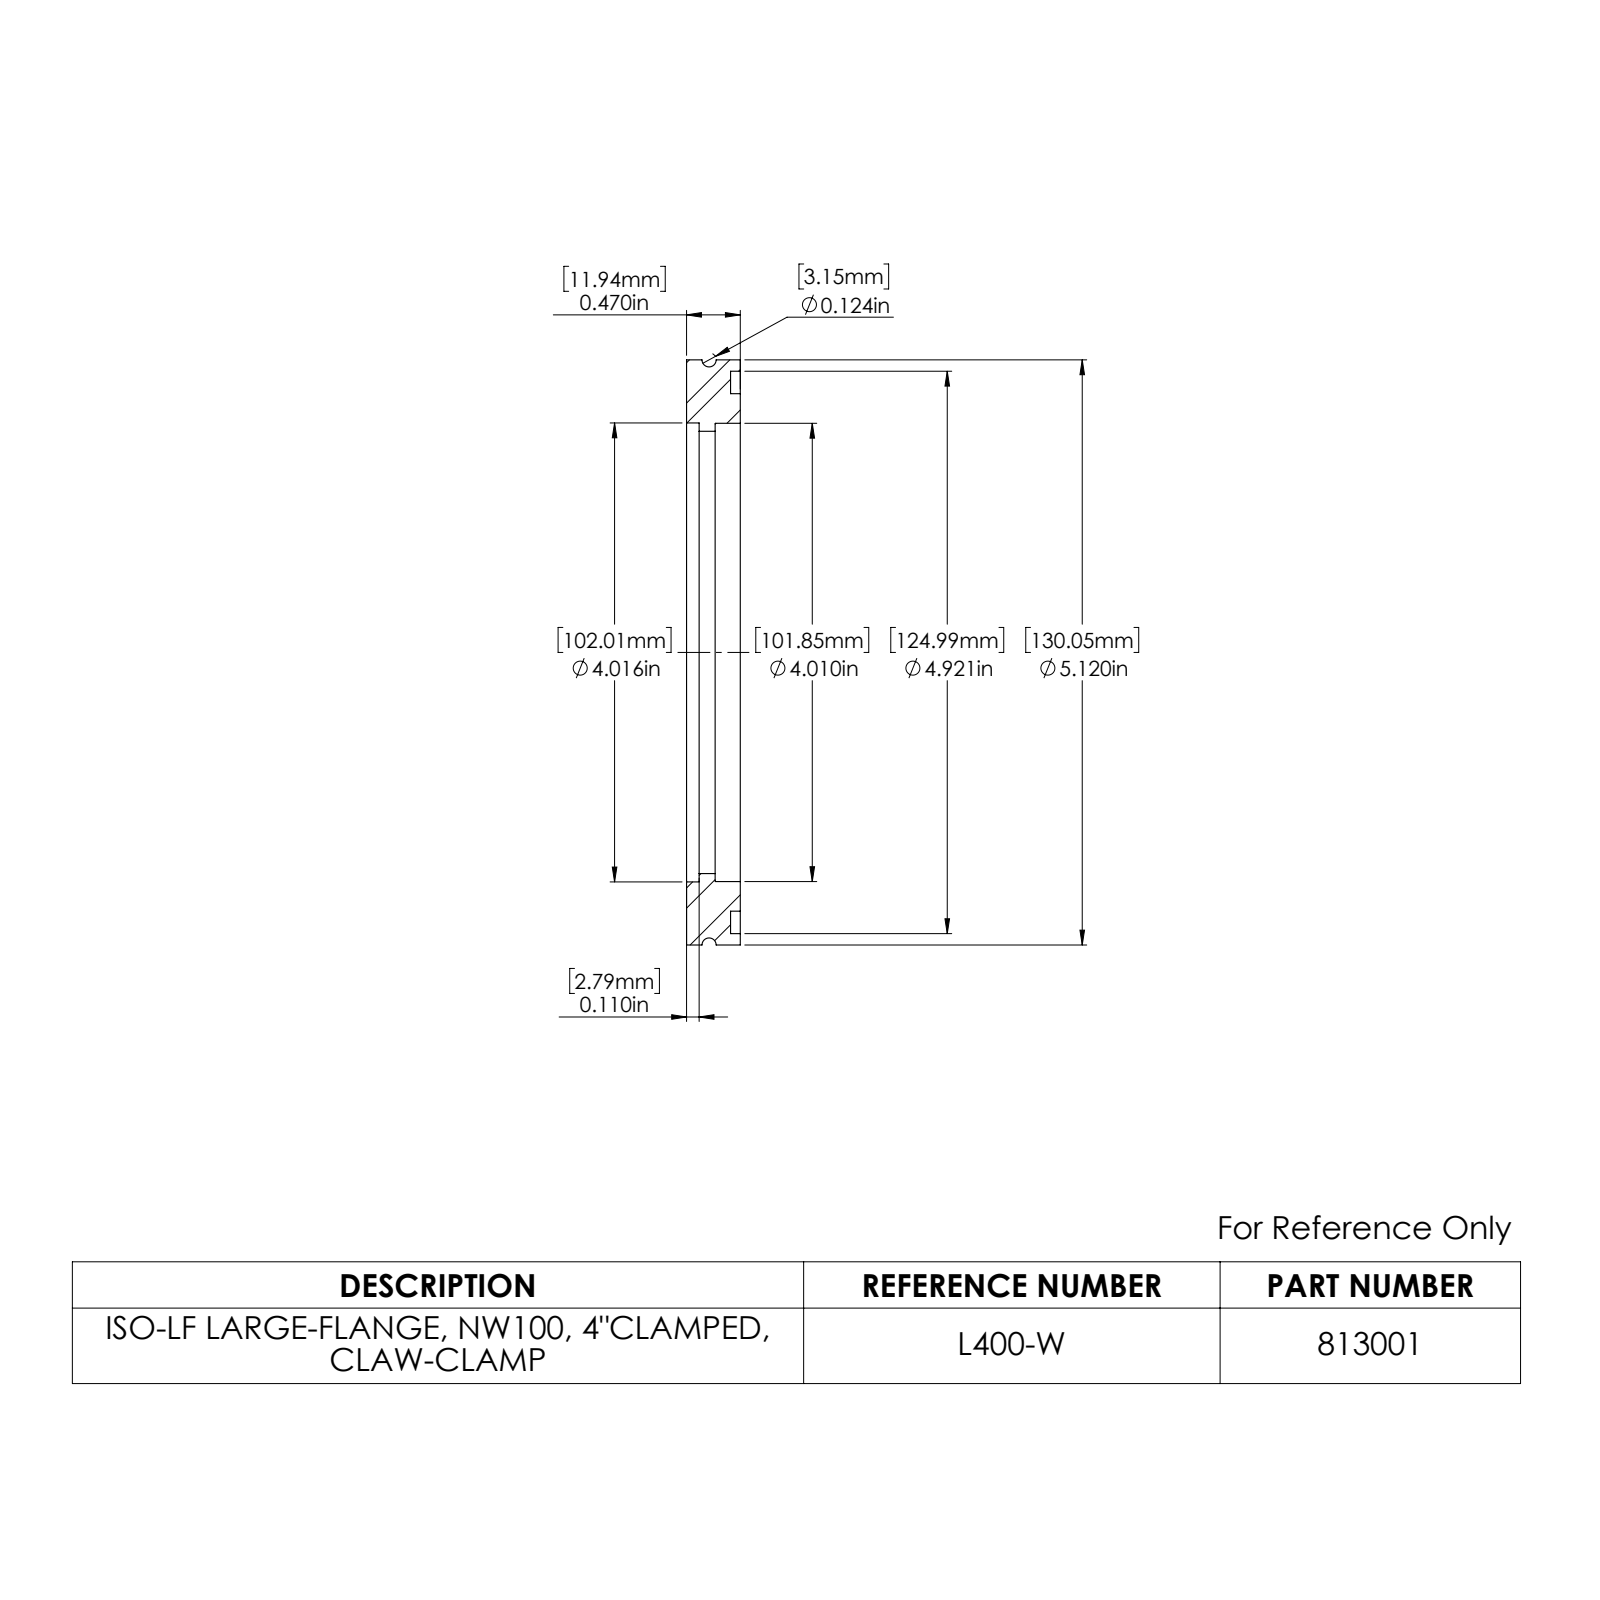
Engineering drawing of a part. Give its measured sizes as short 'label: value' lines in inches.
name: 813001
written by: SolidWorks 2022 (CONFIG_CONTROL_DESIGN)
unit: in
bodies: 1 solid, 26 faces (6 planar, 14 cylindrical, 6 other)
size: 5.12 × 5.12 × 0.47
volume: 3.514 in³; area: 34.66 in²
holes: 1× ⌀3.87, 1× ⌀4.01, 1× ⌀4.016, 1× ⌀4.921
bosses: 1× ⌀5.12, 1× ⌀4.528
face distances: 0.47, 0.085, 0.385, 0.36, 0.275, 0.11, 0.22, 0.135, 0.14, 0.25
